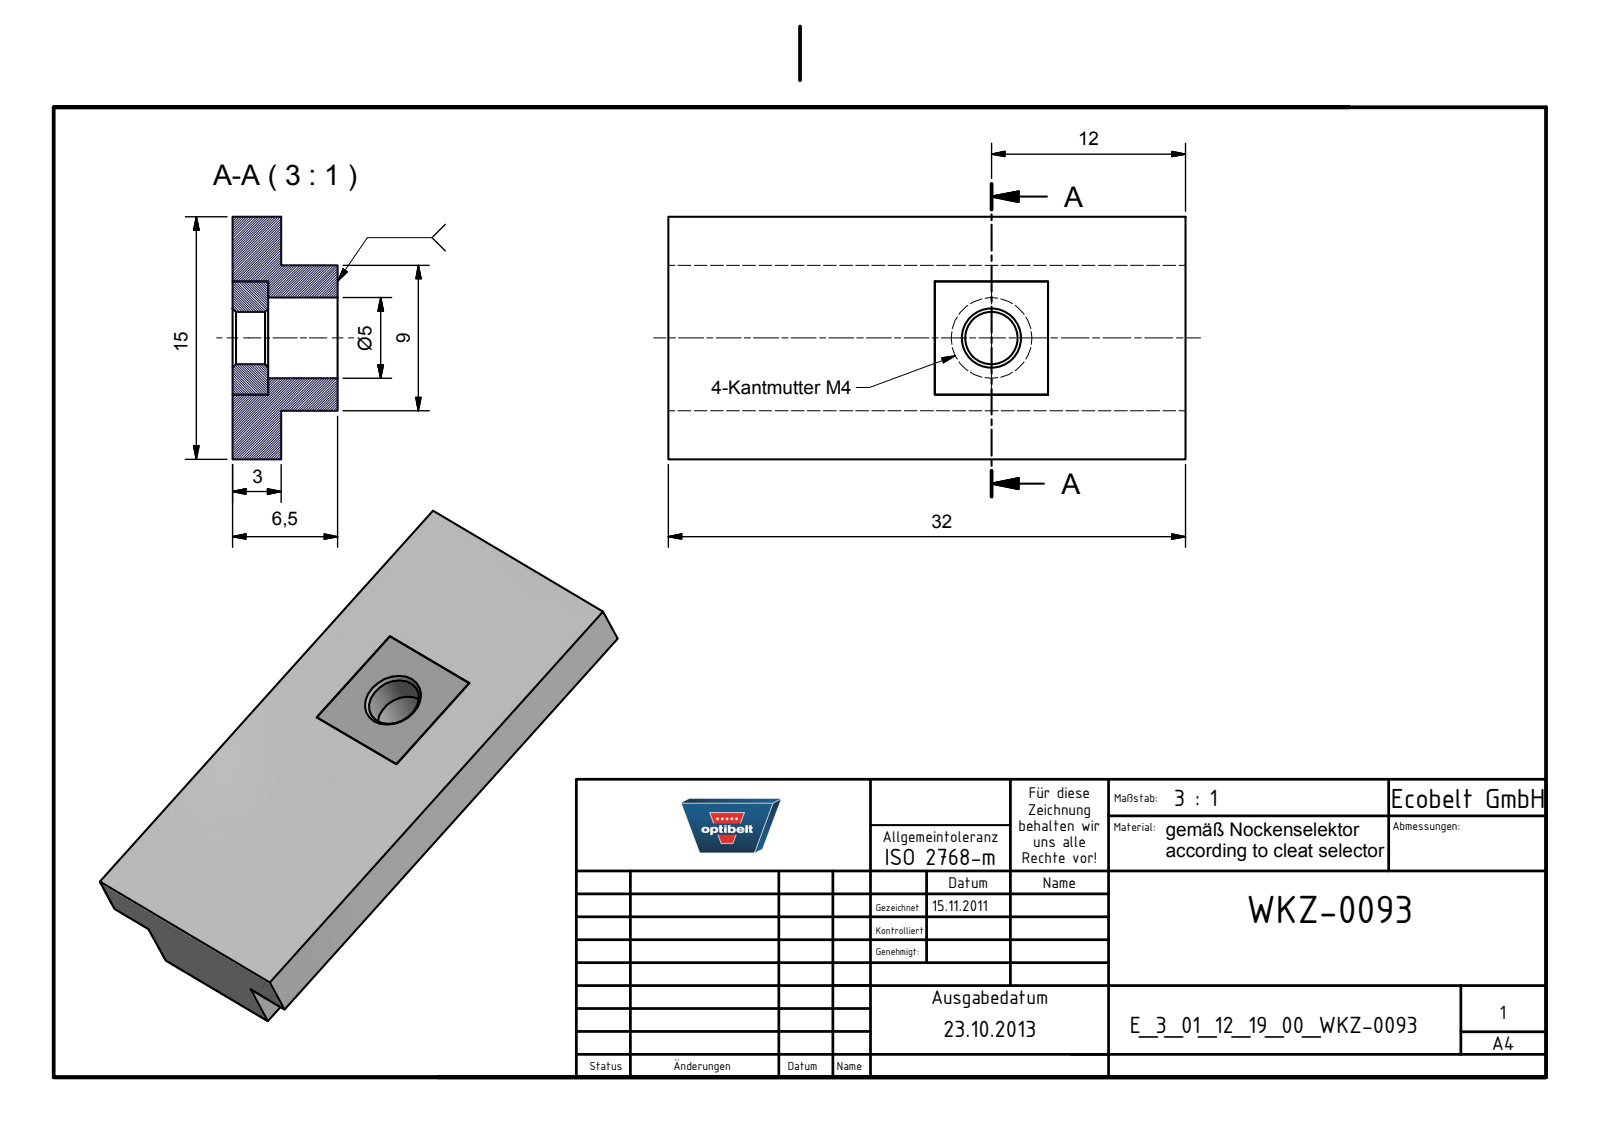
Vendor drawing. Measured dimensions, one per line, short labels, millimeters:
name: E_3_01_12_19_00_WKZ-0093; E_3_01_12_19_00_WKZ-0093-Teil1; E_3_01_12_19_00_WKZ-0093-Teil2
written by: Autodesk Inventor 2025 (AUTOMOTIVE_DESIGN)
unit: mm
bodies: 2 solids, 25 faces (21 planar, 2 cylindrical, 2 other)
size: 32 × 15 × 6.5
volume: 2 345 mm³; area: 1 782 mm²
holes: 1× ⌀3.24, 1× ⌀5
face distances: 3, 6.5, 12, 3.5, 9, 15, 32, 2.2, 0.8, 4.3
